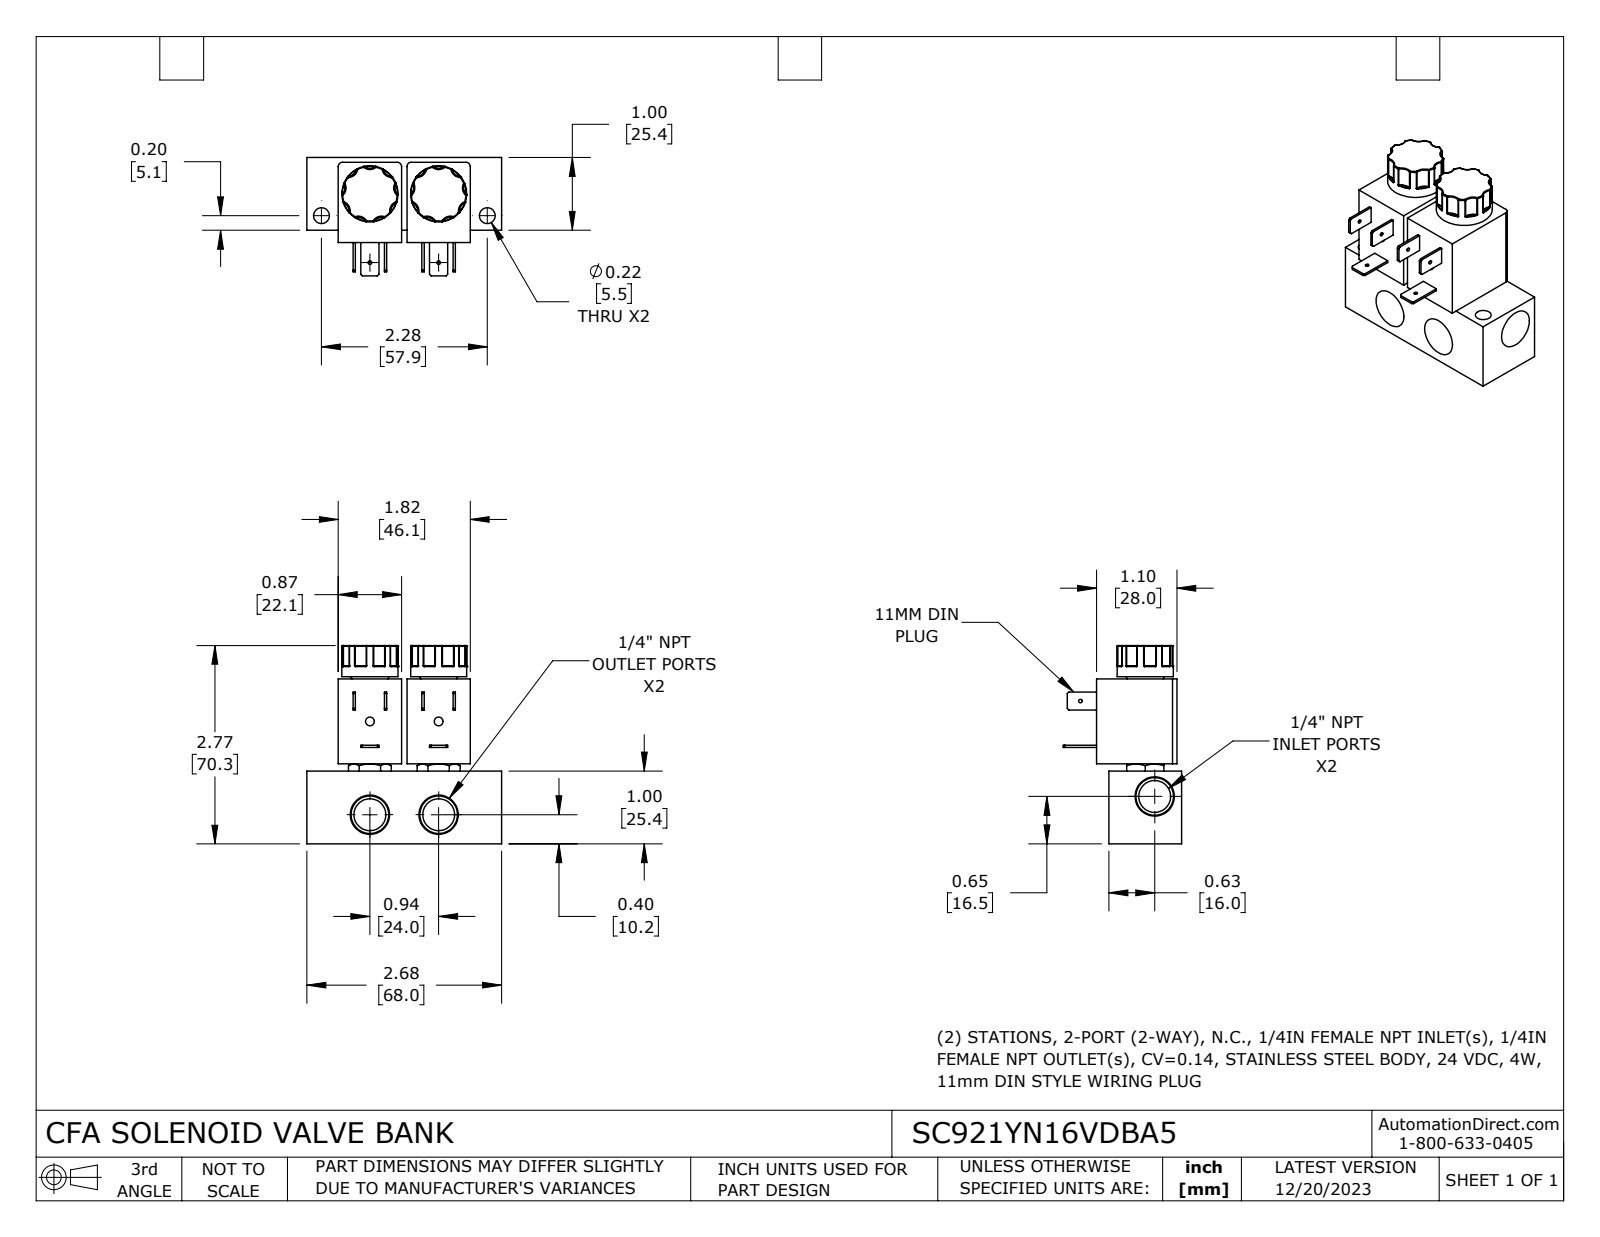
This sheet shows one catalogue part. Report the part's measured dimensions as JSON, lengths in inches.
{"part_name": "SC921YN16VDBA5", "step_written_by": "SolidWorks 2023 (CONFIG_CONTROL_DESIGN)", "units": "inches", "bodies": {"solids": 1, "faces": 446, "planar": 100, "cylindrical": 96, "other": 250}, "overall_size": [2.725, 2.677, 1.627], "volume_in3": 4.833, "surface_area_in2": 34.57, "round_holes": [[0.05, 3], [0.438, 3], [0.12, 2], [0.217, 2]], "round_bosses_or_shafts": [[0.77, 2]], "partial_cylinders_radius": [[0.01, 36], [0.133, 18], [0.06, 4]], "face_to_face_distances": [1, 0.945, 0.87, 1.169, 0.169, 0.065, 0.935, 1.104, 0.431, 1.301], "hole_center_spacings": [0.945, 1.282, 1.593, 0.928, 0.93, 1.662, 1.735, 1.738]}
